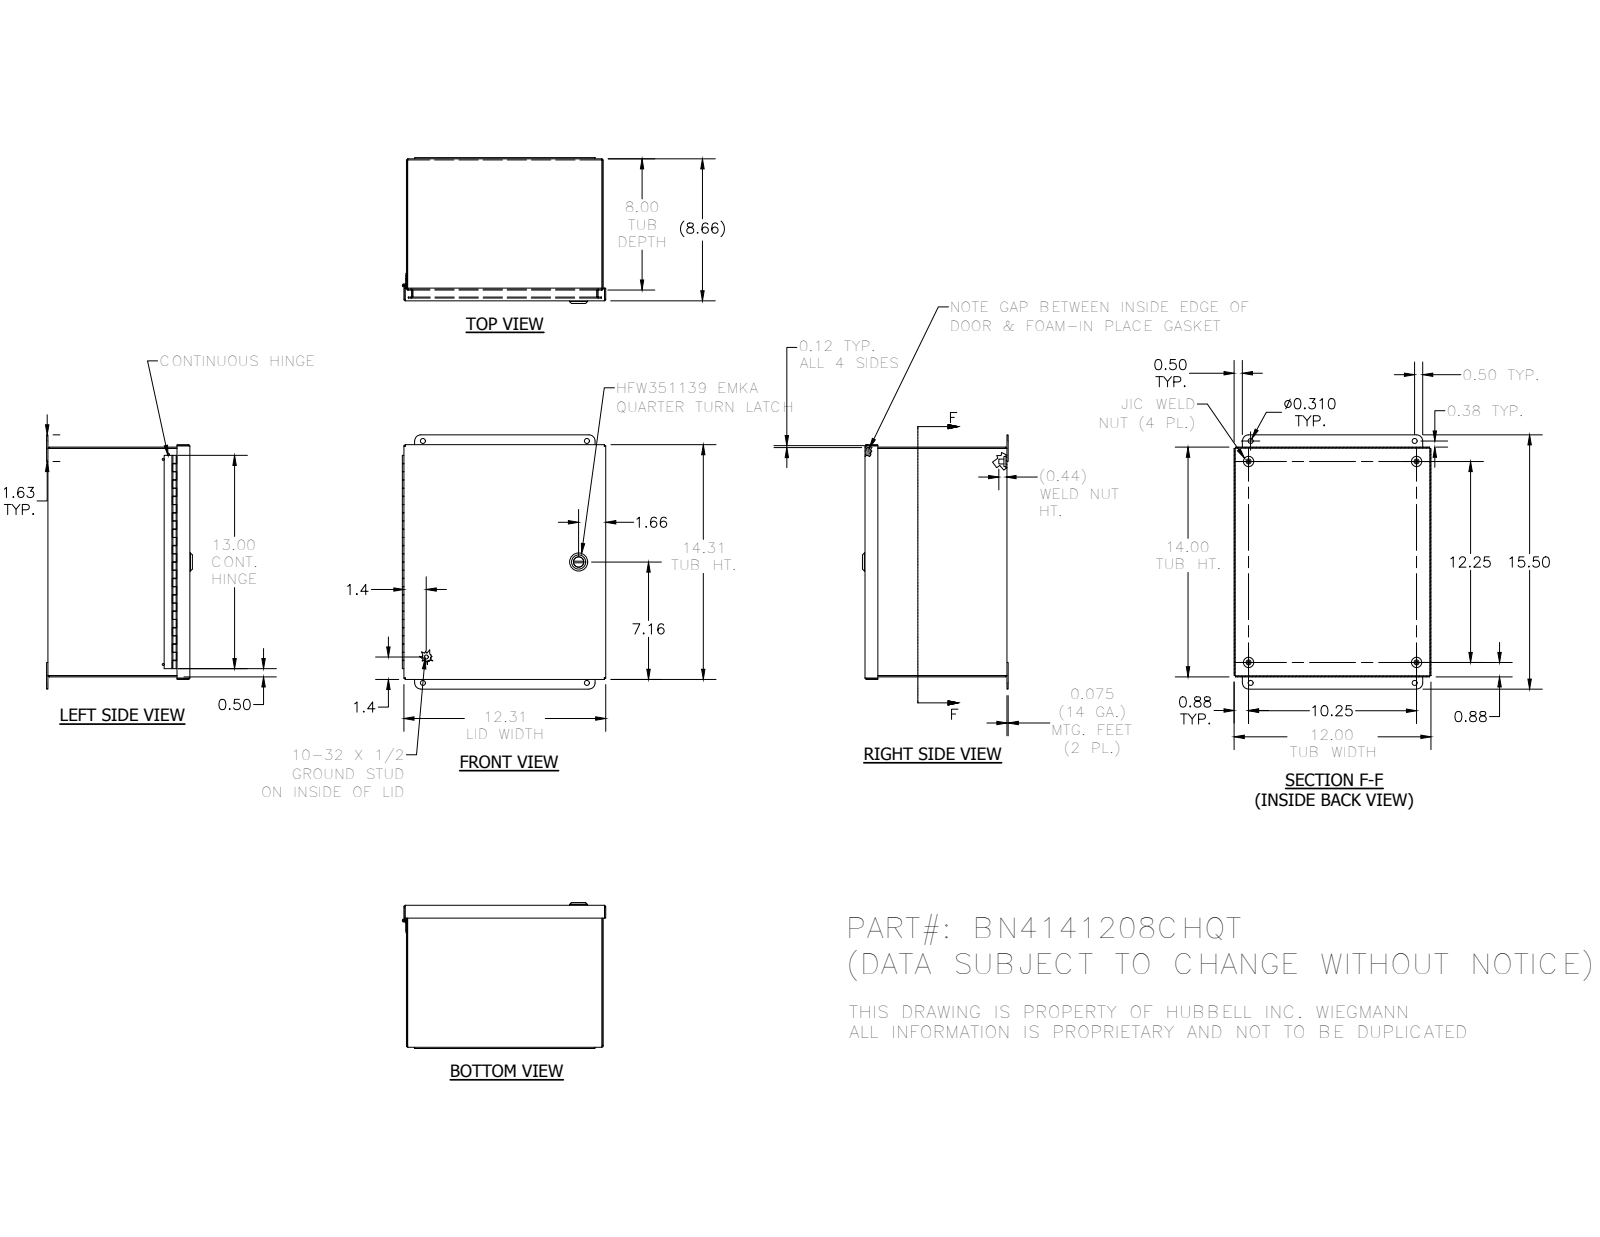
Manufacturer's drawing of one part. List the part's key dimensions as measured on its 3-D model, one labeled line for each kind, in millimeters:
Part name (STEP PRODUCT): BN4141208CHQT
STEP written by: SolidWorks 2018 (AUTOMOTIVE_DESIGN)
Units: millimetres
Bodies: 21 solids, 805 faces (408 planar, 269 cylindrical, 128 other)
Overall size (bounding box): 393.7 × 315.1 × 225.8
Volume: 1 002 000 mm³ · Surface area: 1 217 000 mm²
Round holes (diameter × count): ⌀4 ×4, ⌀7.9 ×4, ⌀3 ×3, ⌀2.9 ×1, ⌀5 ×1, ⌀8 ×1, ⌀10 ×1, ⌀10.2 ×1, ⌀16.1 ×1, ⌀20.4 ×1
Round bosses / shafts (diameter × count): ⌀7.6 ×4, ⌀15.9 ×3, ⌀28 ×1, ⌀22 ×1, ⌀19.8 ×1, ⌀15.9 ×1, ⌀15.8 ×1, ⌀15.2 ×1
Partial cylindrical surfaces — rounded edges, fillets, slot ends (radius × count): R0.3 ×30, R0.8 ×20, R2.4 ×20, R3.2 ×16, R0.5 ×12, R4 ×4, R9.5 ×4, R0.4 ×2
Main face-to-face distances: 1.6, 1.6, 354, 218.3, 219.9, 216.7, 218.3, 303.2, 301.7, 304.8
Hole centre spacings: 428.6, 31.9, 254, 259.1, 259.1, 260.4, 311.2, 342.9
